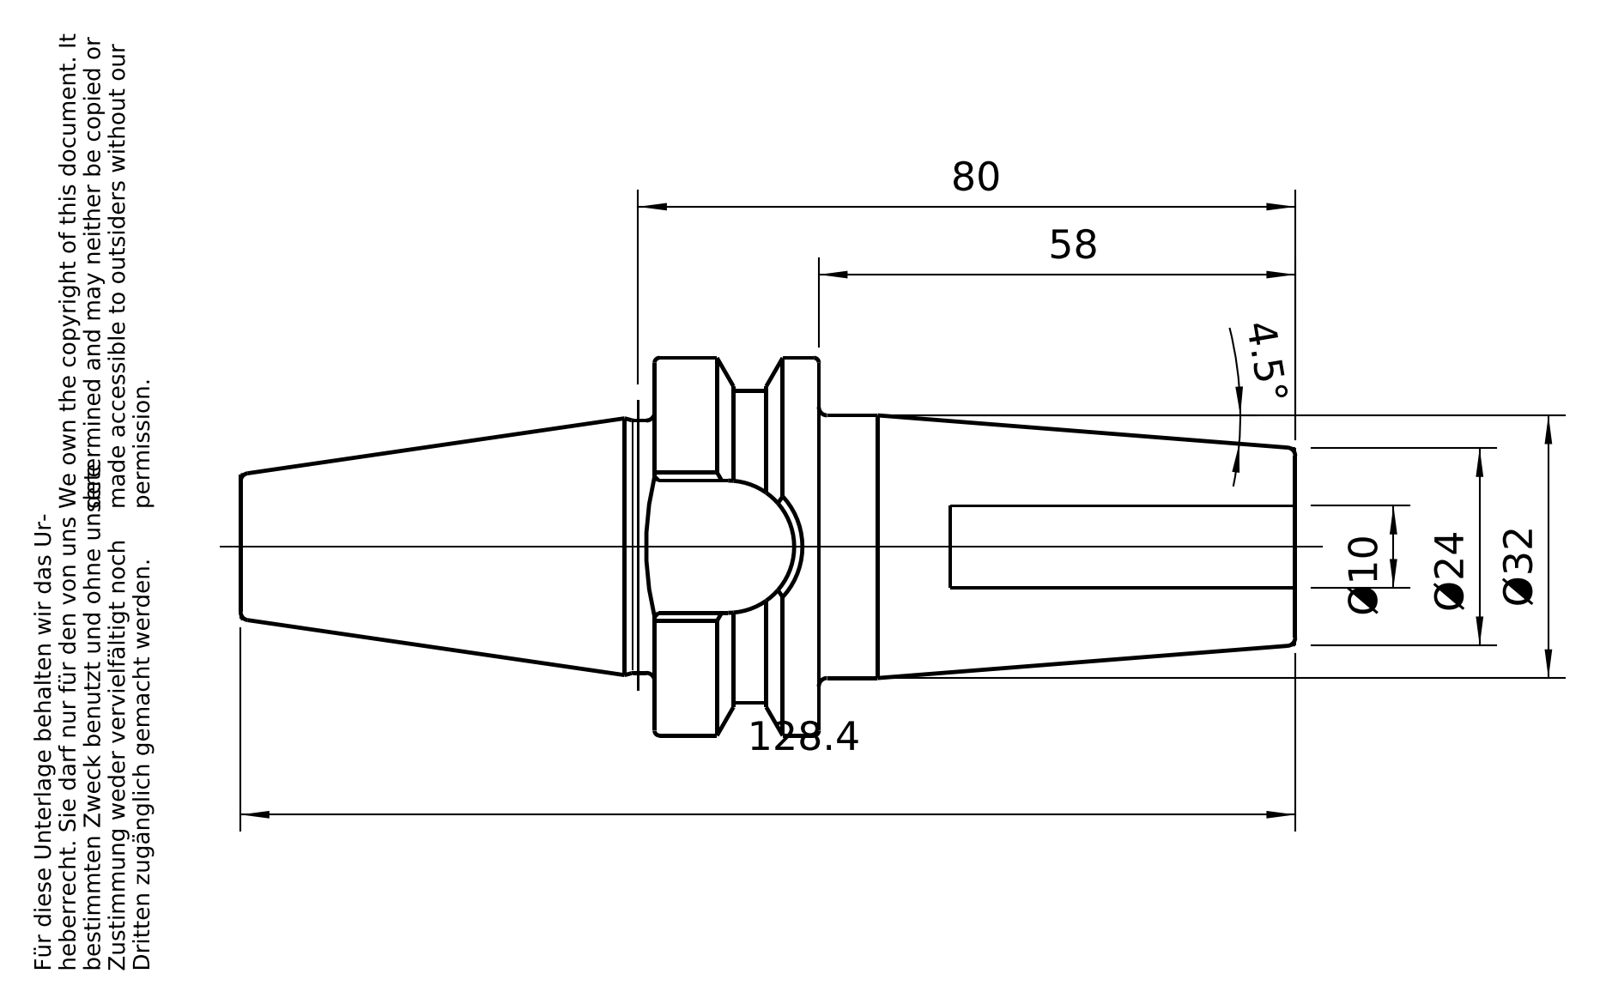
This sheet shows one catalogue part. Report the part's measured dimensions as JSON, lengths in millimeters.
{"part_name": "30-640-10", "step_written_by": "PRO/ENGINEER BY PARAMETRIC TECHNOLOGY CORPORATION, 2010430 (CONFIG_CONTROL_DESIGN)", "units": "millimeters", "bodies": {"solids": 1, "faces": 96, "planar": 26, "cylindrical": 22, "other": 48}, "overall_size": [128.4, 45.98, 45.98], "volume_mm3": 83511, "surface_area_mm2": 17948, "round_holes": [[10, 1], [10.11, 1], [12.51, 1], [13, 1]], "round_bosses_or_shafts": [[45.98, 1], [32, 1], [30.75, 1], [12.01, 1]], "partial_cylinders_radius": [[8.1, 1], [18.88, 1]], "face_to_face_distances": [20, 78, 58, 32.3, 36, 16, 42, 16.2, 50.4, 70.4]}
